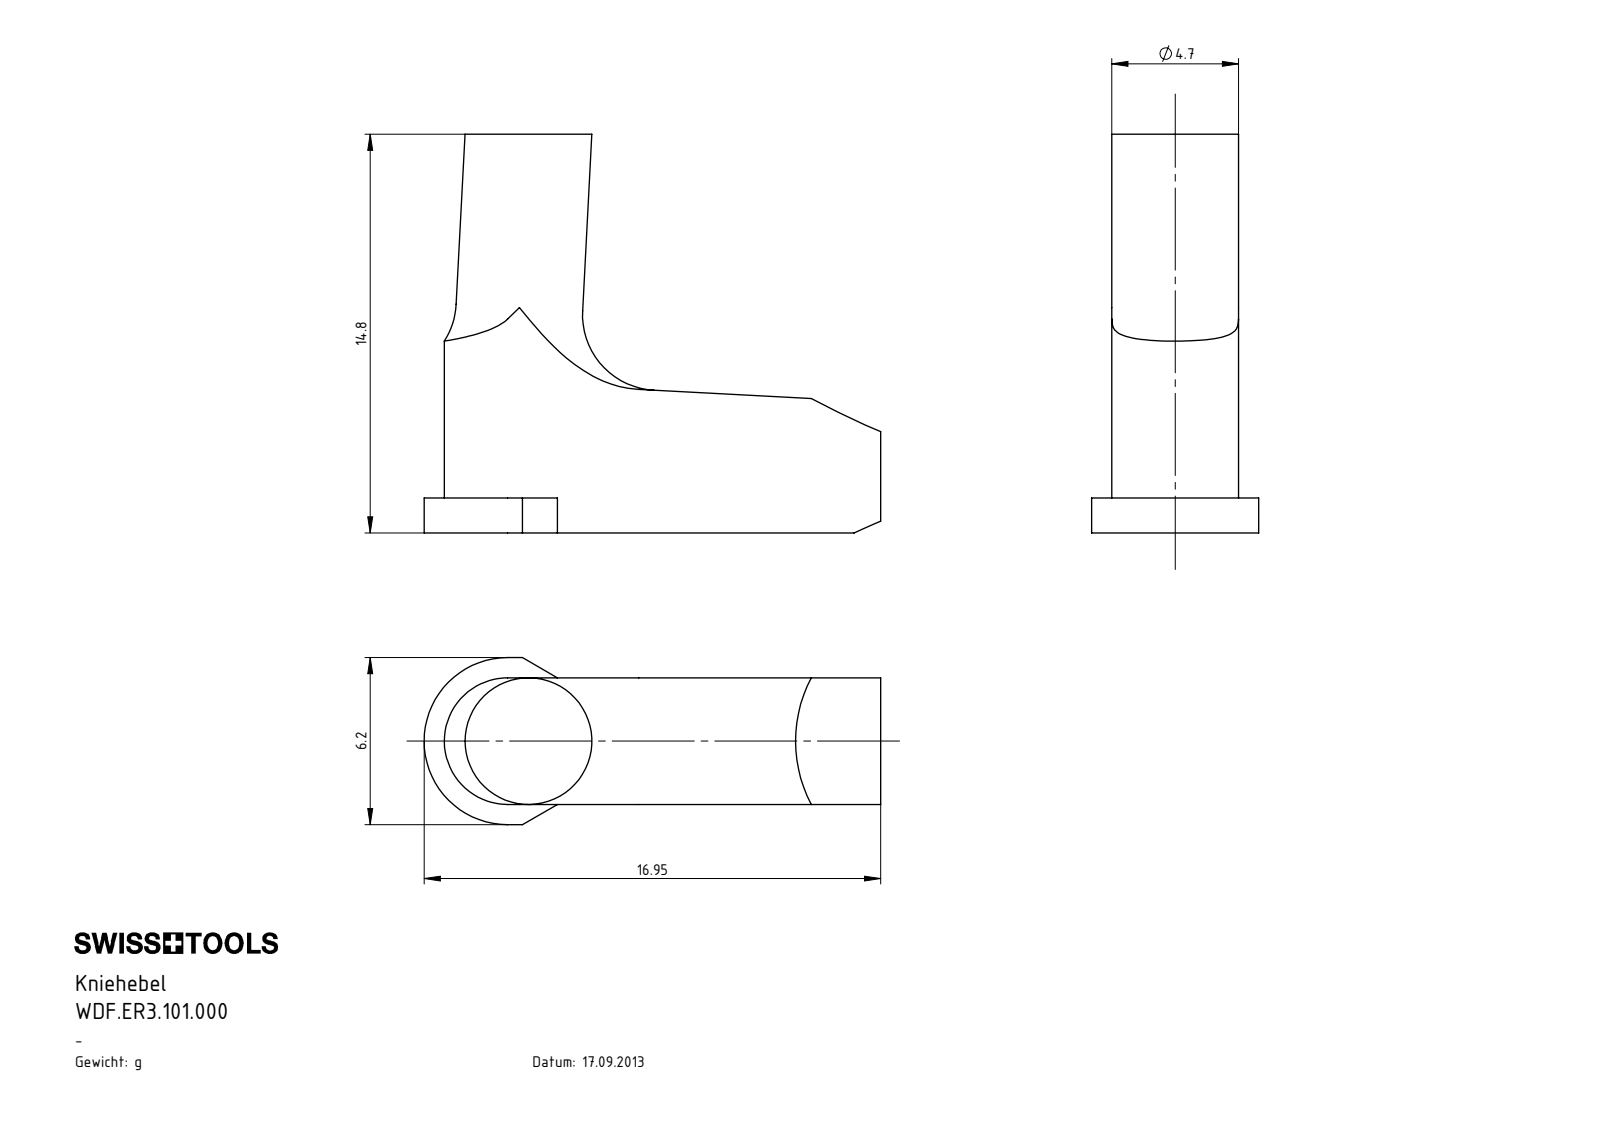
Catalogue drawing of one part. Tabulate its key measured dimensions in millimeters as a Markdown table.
| quantity | value |
| --- | --- |
| part name | WDF.ER3.101.000 |
| STEP written by | SolidWorks 2017 (AUTOMOTIVE_DESIGN) |
| units | millimeters |
| bodies | 1 solid, 18 faces (11 planar, 3 cylindrical, 4 other) |
| overall size | 16.95 × 14.8 × 6.2 |
| volume | 559 mm³ |
| surface area | 501 mm² |
| round bosses / shafts (diameter × count) | 4.7 × 1 |
| partial cylindrical surfaces (radius × count) | 2.35 × 1, 3.1 × 1 |
| main face-to-face distances | 4.7, 14.8, 1.3, 13.5, 0.75, 5.45, 6.2 |
